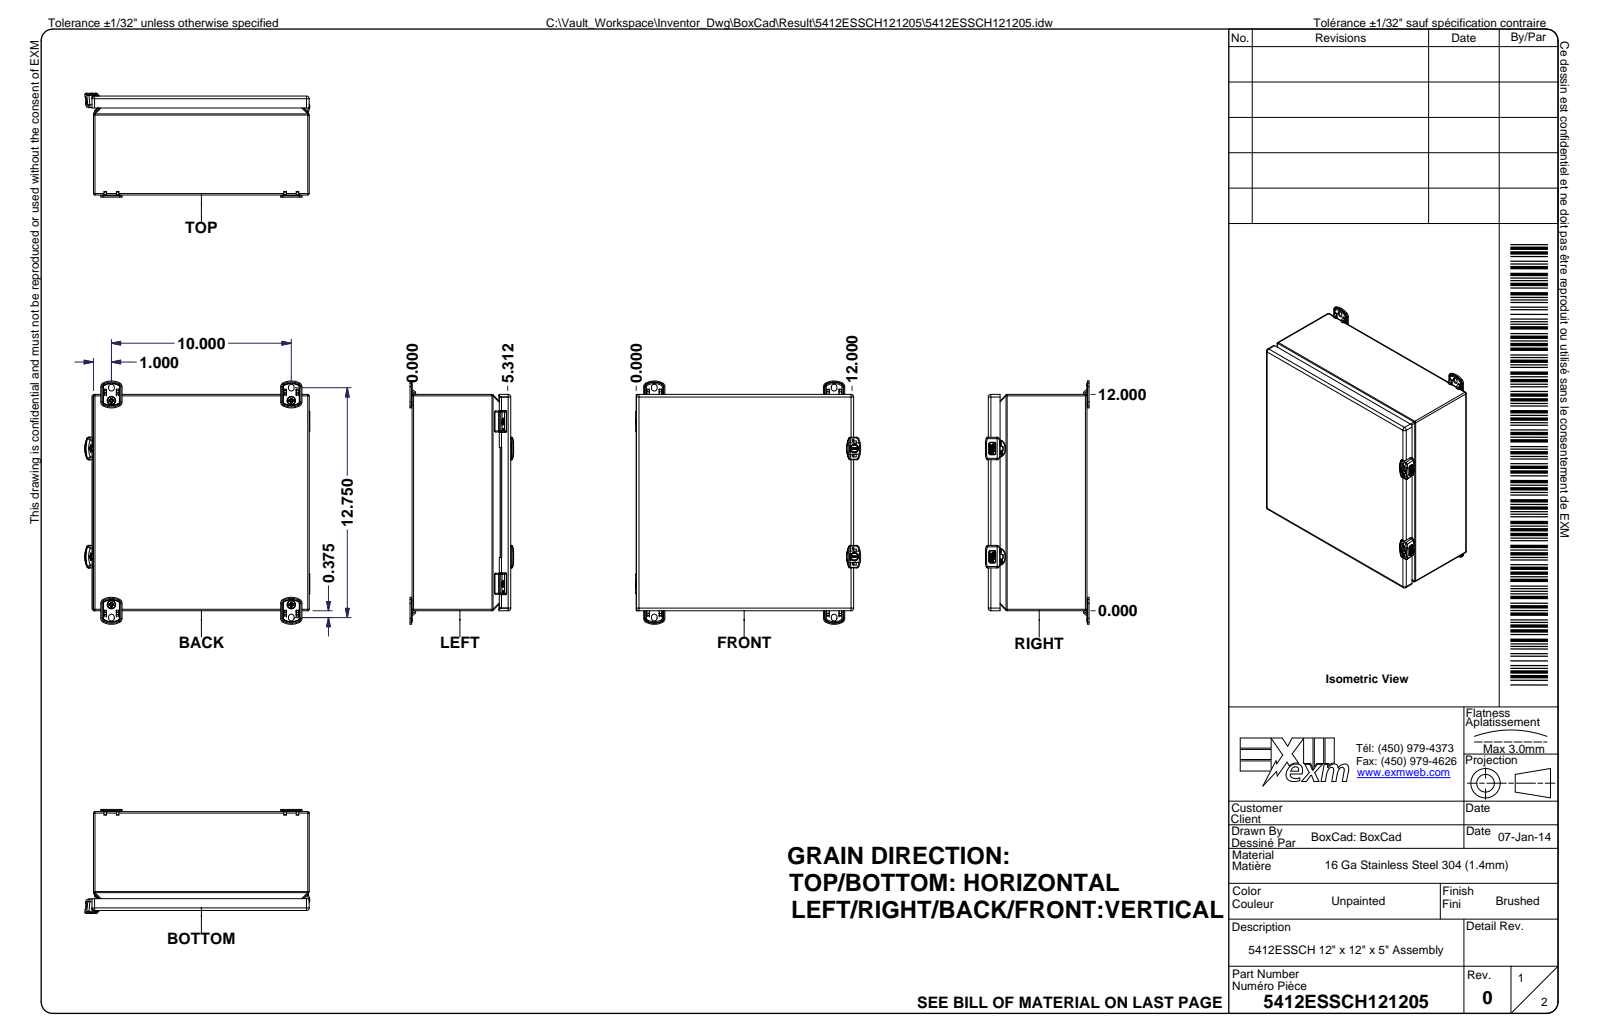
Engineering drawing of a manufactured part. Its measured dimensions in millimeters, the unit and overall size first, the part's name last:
Units: millimetres
Overall size (bounding box): 342.8 × 316 × 146.2
Round holes (diameter × count): ⌀5.1 ×7, ⌀0.8 ×6, ⌀6.1 ×6, ⌀5 ×4, ⌀7.9 ×4, ⌀8.1 ×4, ⌀4.2 ×2, ⌀4.4 ×2, ⌀5.5 ×2, ⌀6 ×2, ⌀10.7 ×2, ⌀3.2 ×1
Round bosses / shafts (diameter × count): ⌀5.9 ×8, ⌀10 ×6, ⌀0.9 ×6, ⌀13 ×4, ⌀12.7 ×4, ⌀5 ×3, ⌀10.5 ×2, ⌀8.4 ×2
Partial cylindrical surfaces — rounded edges, fillets, slot ends (radius × count): R0.2 ×252, R0.5 ×97, R0.1 ×84, R0.3 ×83, R1 ×56, R0.3 ×44, R0.8 ×34, R1.5 ×27
Main face-to-face distances: 1.3, 137.9, 303.5, 136.5, 139.2, 11.4, 126.5, 13.1, 10, 127.9
Hole centre spacings: 260.4, 260.4, 368.2, 13.9, 257.5, 273.8, 375.7, 59.2
Volume: 702 800 mm³ · Surface area: 980 000 mm²
Bodies: 47 solids, 7453 faces (3549 planar, 1558 cylindrical, 2346 other)
Part name (STEP PRODUCT): 5412ESSCH121205; 5412ESSCH121205B; 5412ESSCH121205B-P; STK-Q-08500 (+8 more)
STEP written by: Autodesk Inventor 2024 (AUTOMOTIVE_DESIGN)
